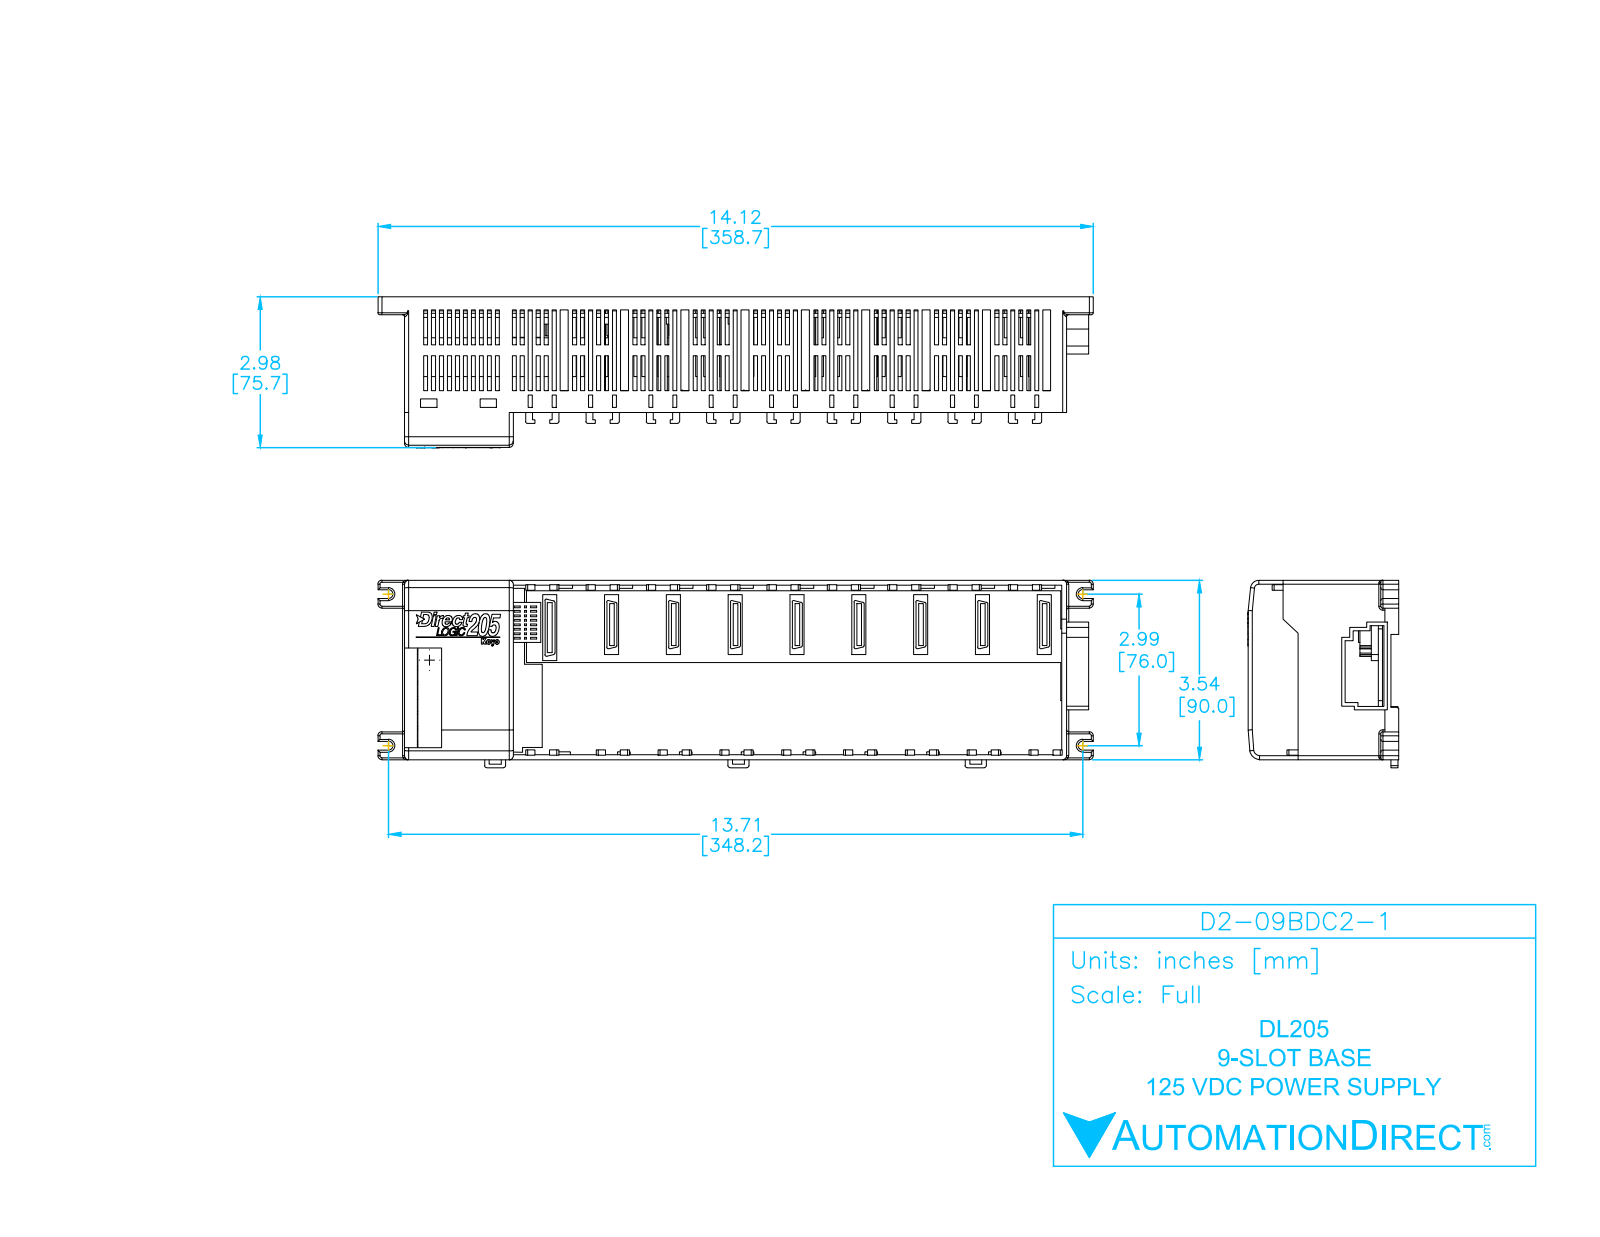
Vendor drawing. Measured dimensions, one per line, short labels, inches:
name: D2-09BDC2-1
written by: SolidWorks 2009 (AUTOMOTIVE_DESIGN)
unit: in
bodies: 7 solids, 3025 faces (2640 planar, 219 cylindrical, 166 other)
size: 14.121 × 3.701 × 2.98
volume: 21.62 in³; area: 390.1 in²
bosses: 6× ⌀0.213
rounds: 86× R0.039, 36× R0.03, 24× R0.01, 20× R0.079, 4× R0.087, 4× R0.185, 1× R0.162, 1× R0.208
face distances: 0.098, 0.118, 3.346, 0.049, 3.445, 0.079, 0.167, 0.246, 0.128, 3.543
